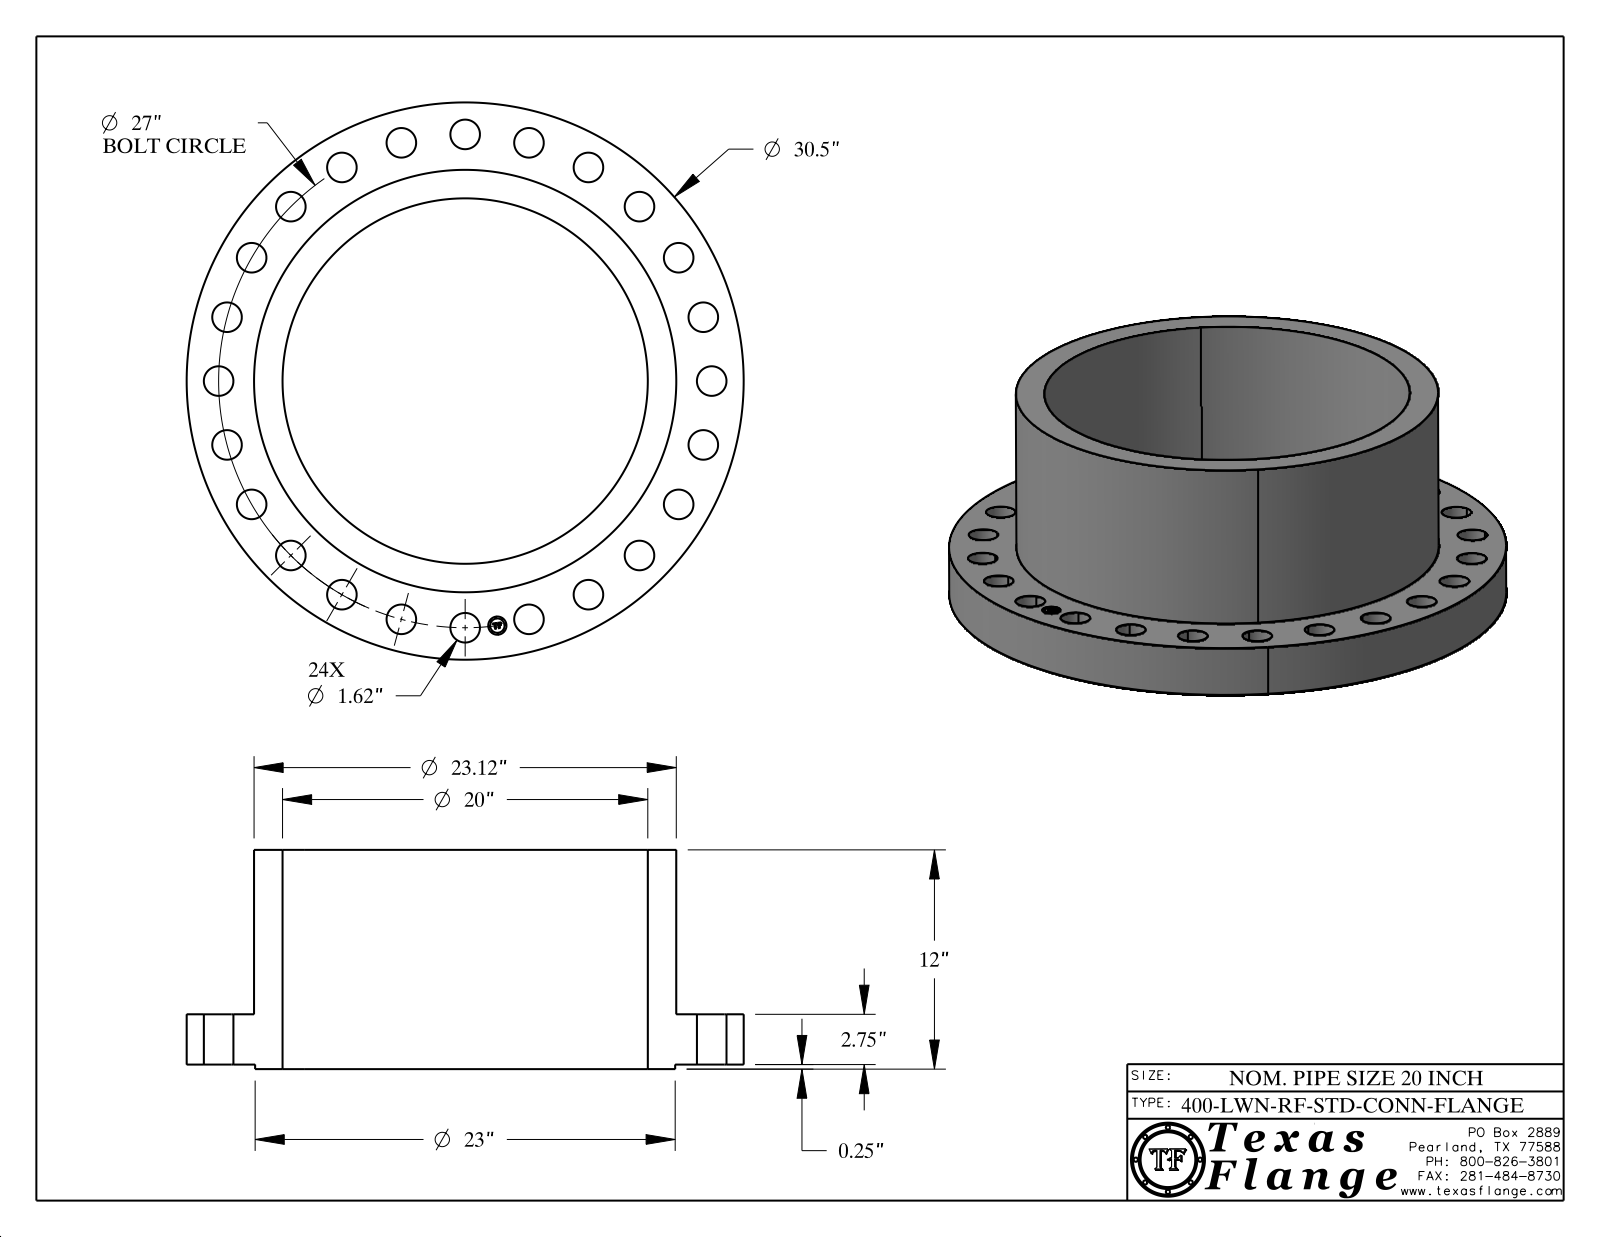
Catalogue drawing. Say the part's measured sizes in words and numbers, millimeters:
The part is named "20-400-LWN-RF-STD-CONN-FLANGE". Its 3-D file was written by "CATIA V5 STEP AP214 (AUTOMOTIVE_DESIGN)". It is 1 solid with 445 faces: 369 planar, 76 cylindrical and 0 other. Overall it measures 774.7 by 774.7 by 304.8 millimeters. Its volume is 32 540 000 cubic millimeters and its surface area 1 780 000 square millimeters. Round holes: 24 of diameter 41.1, 1 of diameter 25.4, 1 of diameter 508. Round bosses or shafts: 8 of diameter 1.5, 1 of diameter 774.7, 1 of diameter 587.2, 1 of diameter 584.2, 1 of diameter 20. The main face-to-face distances are 69.9, 298.5, 228.6, 6.4, 76.2, 304.8, 76.1, 69.7, 228.7, 7.6. The hole center spacings are 342.9, 89.5, 177.5, 262.5, 417.5, 633.6, 679.9, 544.1.
